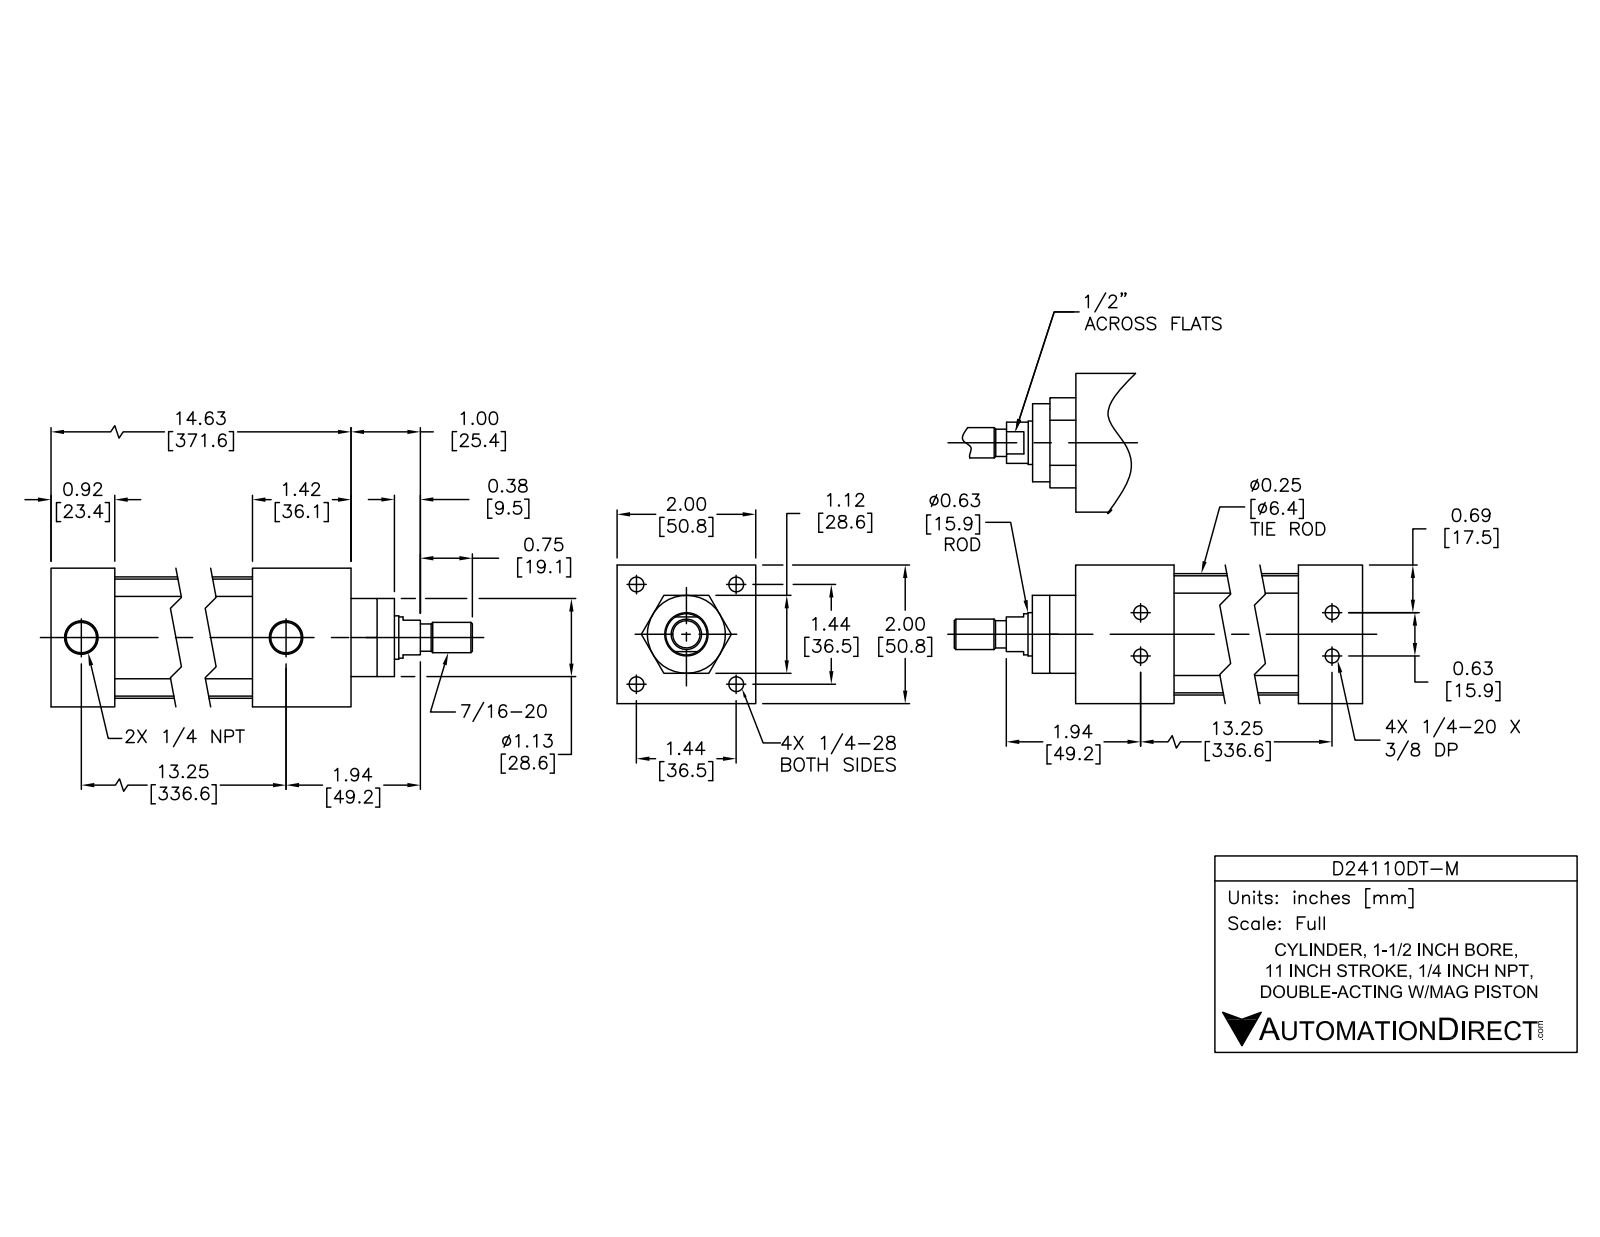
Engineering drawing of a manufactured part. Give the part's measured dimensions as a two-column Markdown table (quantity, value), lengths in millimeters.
| quantity | value |
| --- | --- |
| part name | D24110DT-M PISTON; D24110DT-M; D24110DT-M BODY |
| STEP written by | SolidWorks 2015 (AUTOMOTIVE_DESIGN) |
| units | millimeters |
| bodies | 12 solids, 303 faces (99 planar, 114 cylindrical, 90 other) |
| overall size | 415.8 × 50.8 × 50.8 |
| volume | 405 600 mm³ |
| surface area | 166 200 mm² |
| round holes (diameter × count) | 5 × 4, 5.4 × 4, 7.1 × 4, 10.3 × 4, 7.5 × 2, 12.1 × 2, 15.9 × 1, 16 × 1, 38.1 × 1 |
| round bosses / shafts (diameter × count) | 9.9 × 4, 6.4 × 4, 5.6 × 4, 44.5 × 1, 38 × 1, 28.5 × 1, 15.8 × 1, 15 × 1 |
| partial cylindrical surfaces (radius × count) | 5.1 × 4 |
| main face-to-face distances | 50.8, 2, 309.9, 371.4, 36.1, 335.3, 348, 311.9, 23.4, 28.5 |
| hole center spacings | 36.4, 336.6, 7.9, 8, 15.9, 25.8, 51.5, 336.5 |
